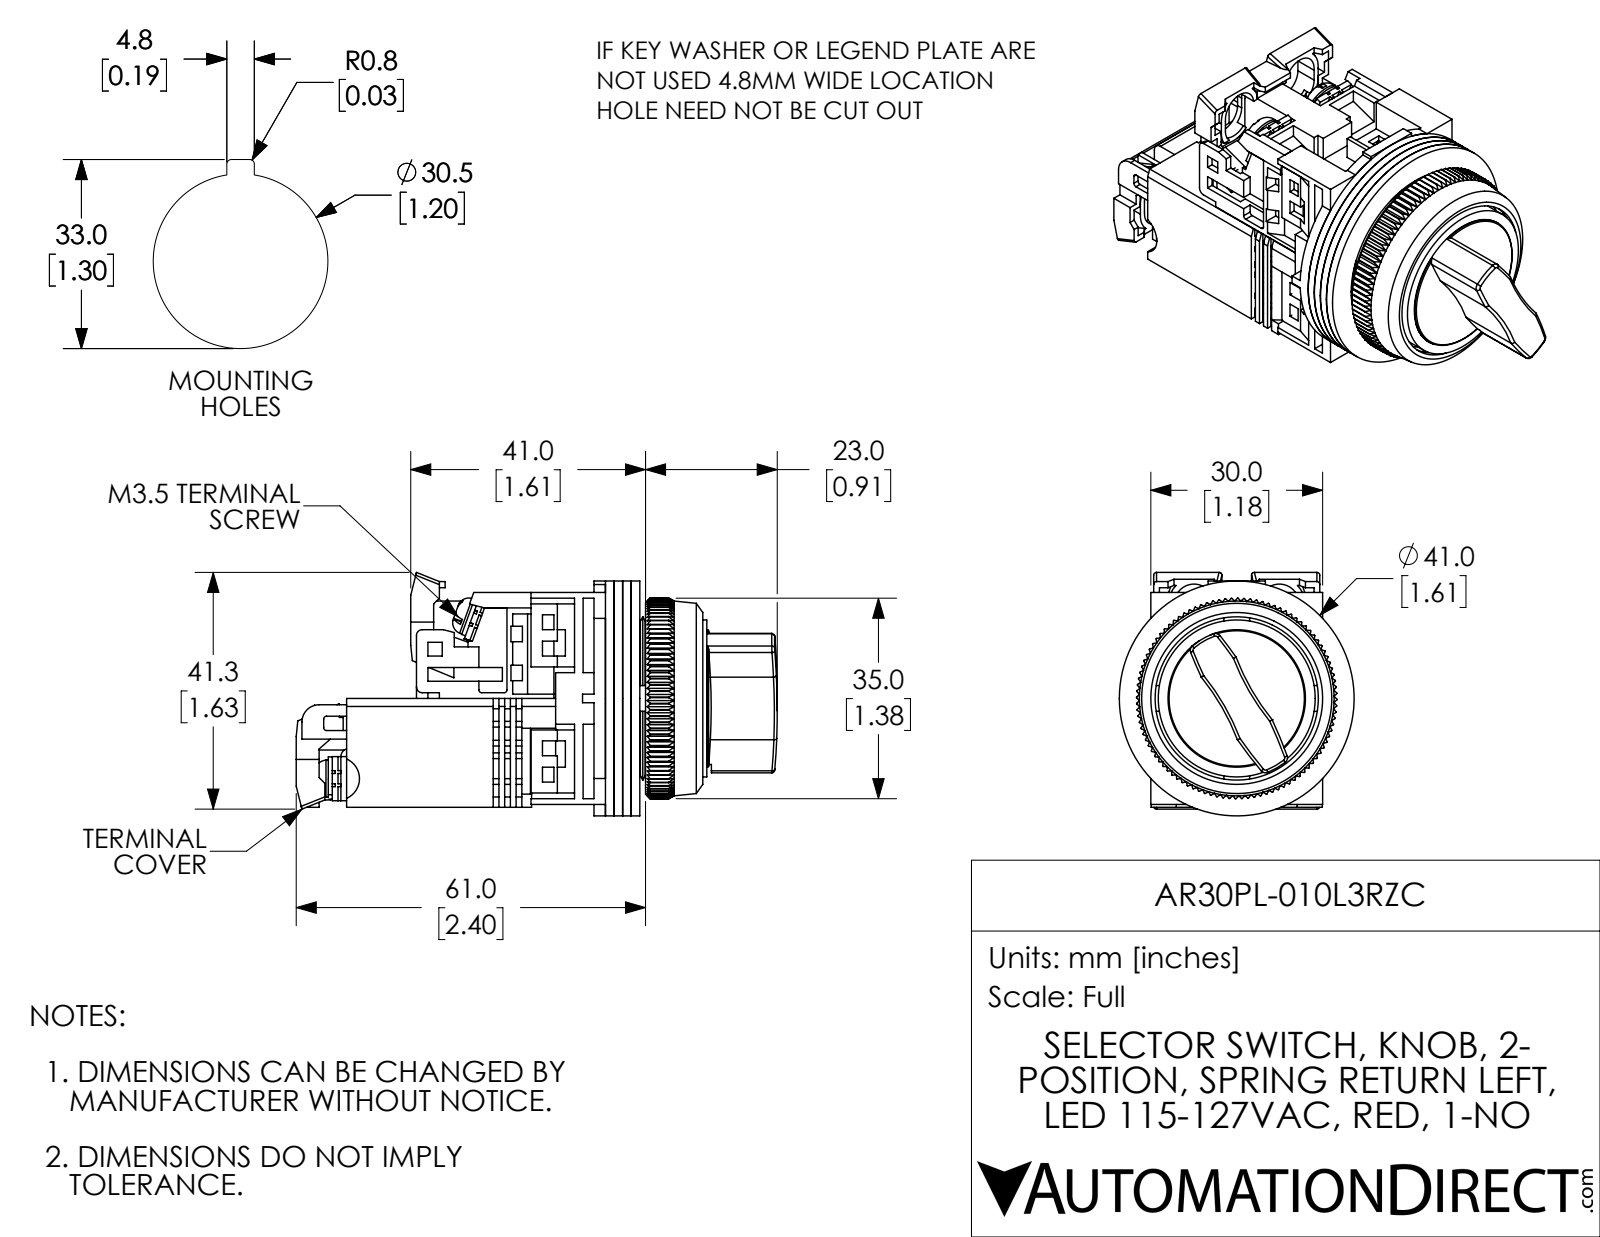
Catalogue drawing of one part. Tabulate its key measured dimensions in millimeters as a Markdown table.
| quantity | value |
| --- | --- |
| part name | AR30PL-010L3RZC |
| STEP written by | SolidWorks 2017 (AUTOMOTIVE_DESIGN) |
| units | millimeters |
| bodies | 27 solids, 2357 faces (1706 planar, 321 cylindrical, 330 other) |
| overall size | 84 × 42.5 × 41 |
| volume | 49 180 mm³ |
| surface area | 40 890 mm² |
| round holes (diameter × count) | 3.5 × 6, 3.6 × 4, 3 × 3, 12 × 1, 18 × 1, 19.5 × 1, 21 × 1, 28.5 × 1, 30 × 1, 31.8 × 1 |
| round bosses / shafts (diameter × count) | 6.6 × 4, 3.5 × 2, 1.6 × 2, 41 × 1, 29.2 × 1, 27.4 × 1, 24 × 1, 22.5 × 1 |
| partial cylindrical surfaces (radius × count) | 1.5 × 17, 0.5 × 13, 1 × 6, 3.5 × 4, 4.5 × 4, 3 × 2, 40 × 2, 75 × 2 |
| main face-to-face distances | 1.5, 3, 4.5, 2, 1, 19, 20, 5, 6.5, 36 |
| hole center spacings | 14.7, 7.5, 15.8, 0.5, 7.7, 14.8, 14.8, 15.4 |
